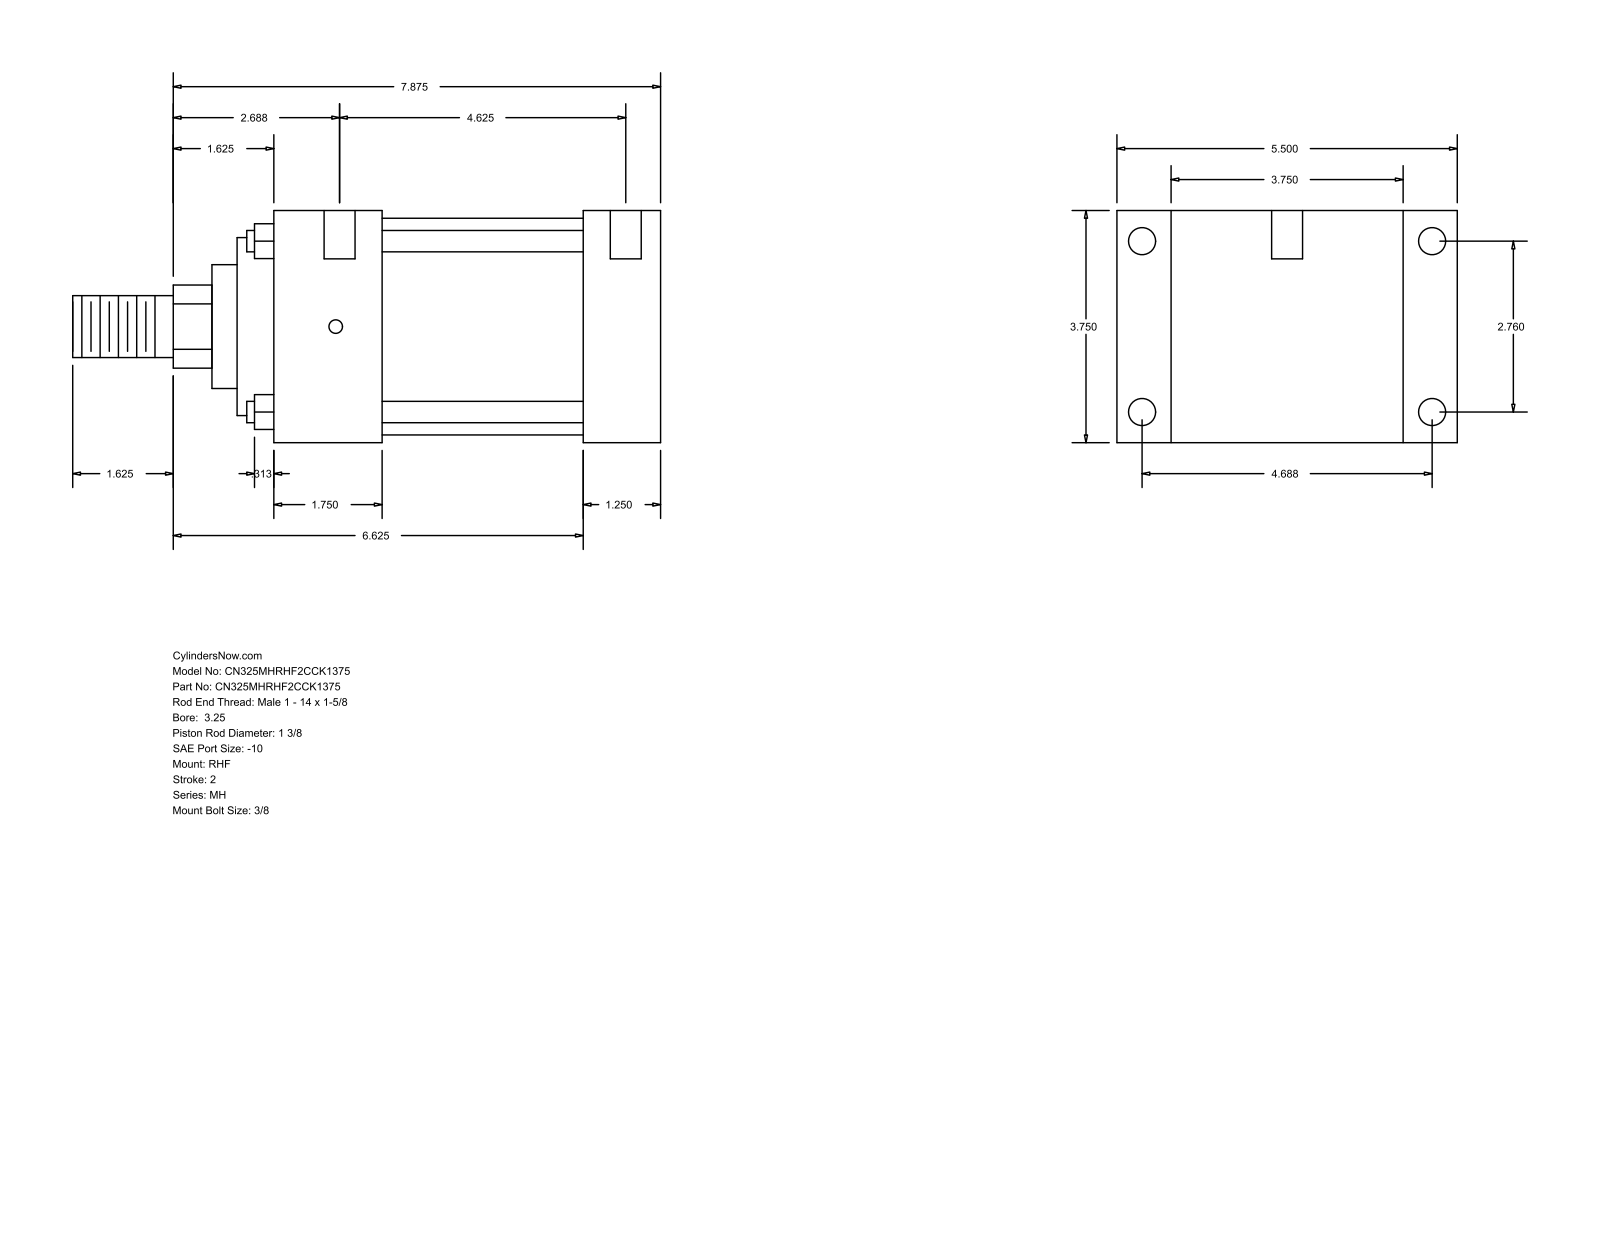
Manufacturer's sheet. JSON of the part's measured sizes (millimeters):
{"part_name": "MH_RHF__0325_1.375", "step_written_by": "GSSL Pune (CONFIG_CONTROL_DESIGN)", "units": "millimeters", "bodies": {"solids": 0, "faces": 90, "planar": 61, "cylindrical": 29, "other": 0}, "overall_size": [241.3, 139.7, 95.25], "round_holes": [[5.56, 4], [11.13, 4], [12.7, 2]], "round_bosses_or_shafts": [[8.76, 4], [88.9, 1], [73.03, 1], [50.8, 1], [34.92, 1], [25.4, 1]], "partial_cylinders_radius": [[17.06, 1]], "face_to_face_distances": [95.24, 31.75, 22.23, 117.47, 127.01, 158.76, 139.7, 44.45, 82.56, 114.31], "hole_center_spacings": [70.1, 119.06, 123.83, 138.16, 1.59, 4.76, 117.48, 119.07]}
